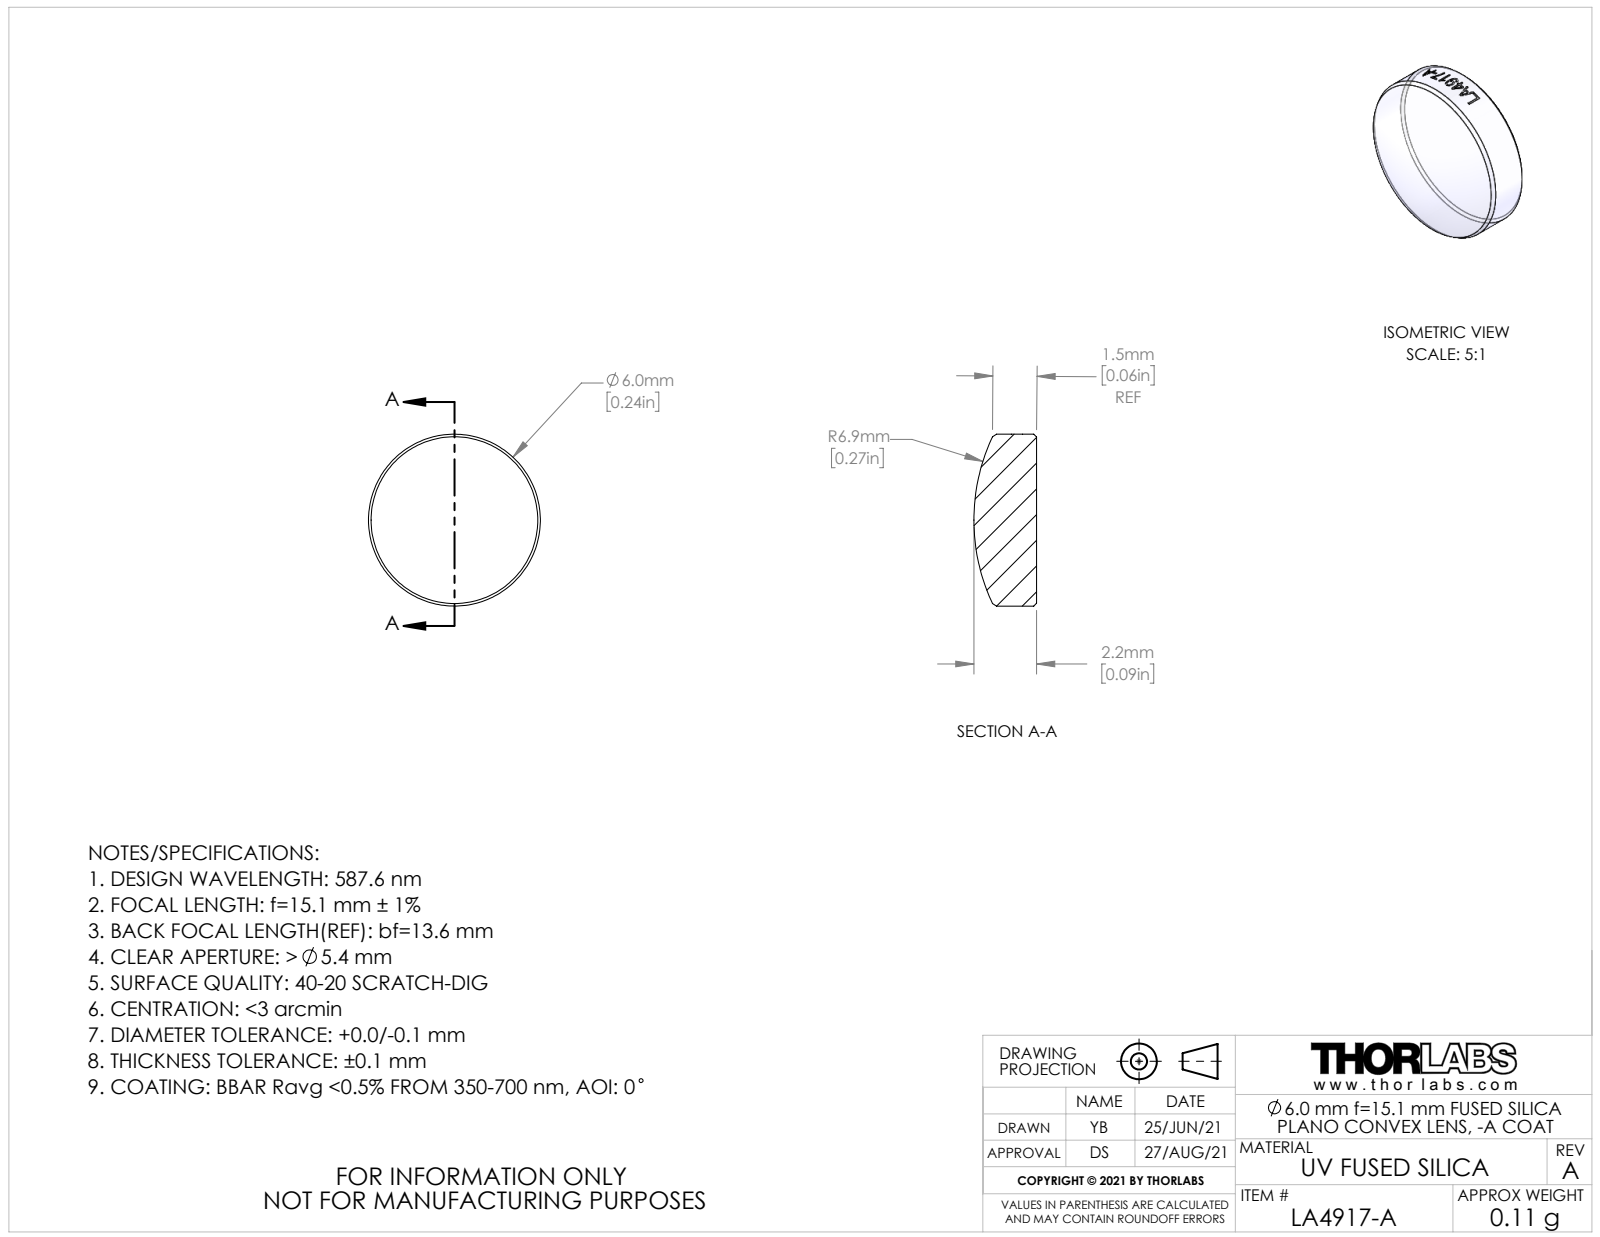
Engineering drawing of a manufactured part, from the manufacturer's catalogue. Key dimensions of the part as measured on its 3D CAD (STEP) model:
Part name (STEP PRODUCT): CTN017551; CTN017508-E0W
STEP written by: SolidWorks 2018 (AUTOMOTIVE_DESIGN)
Units: millimetres
Bodies: 1 solid, 21 faces (1 planar, 14 cylindrical, 6 other)
Overall size (bounding box): 6 × 6 × 2.19
Volume: 52 mm³ · Surface area: 85 mm²
Round bosses / shafts (diameter × count): ⌀6 ×1
